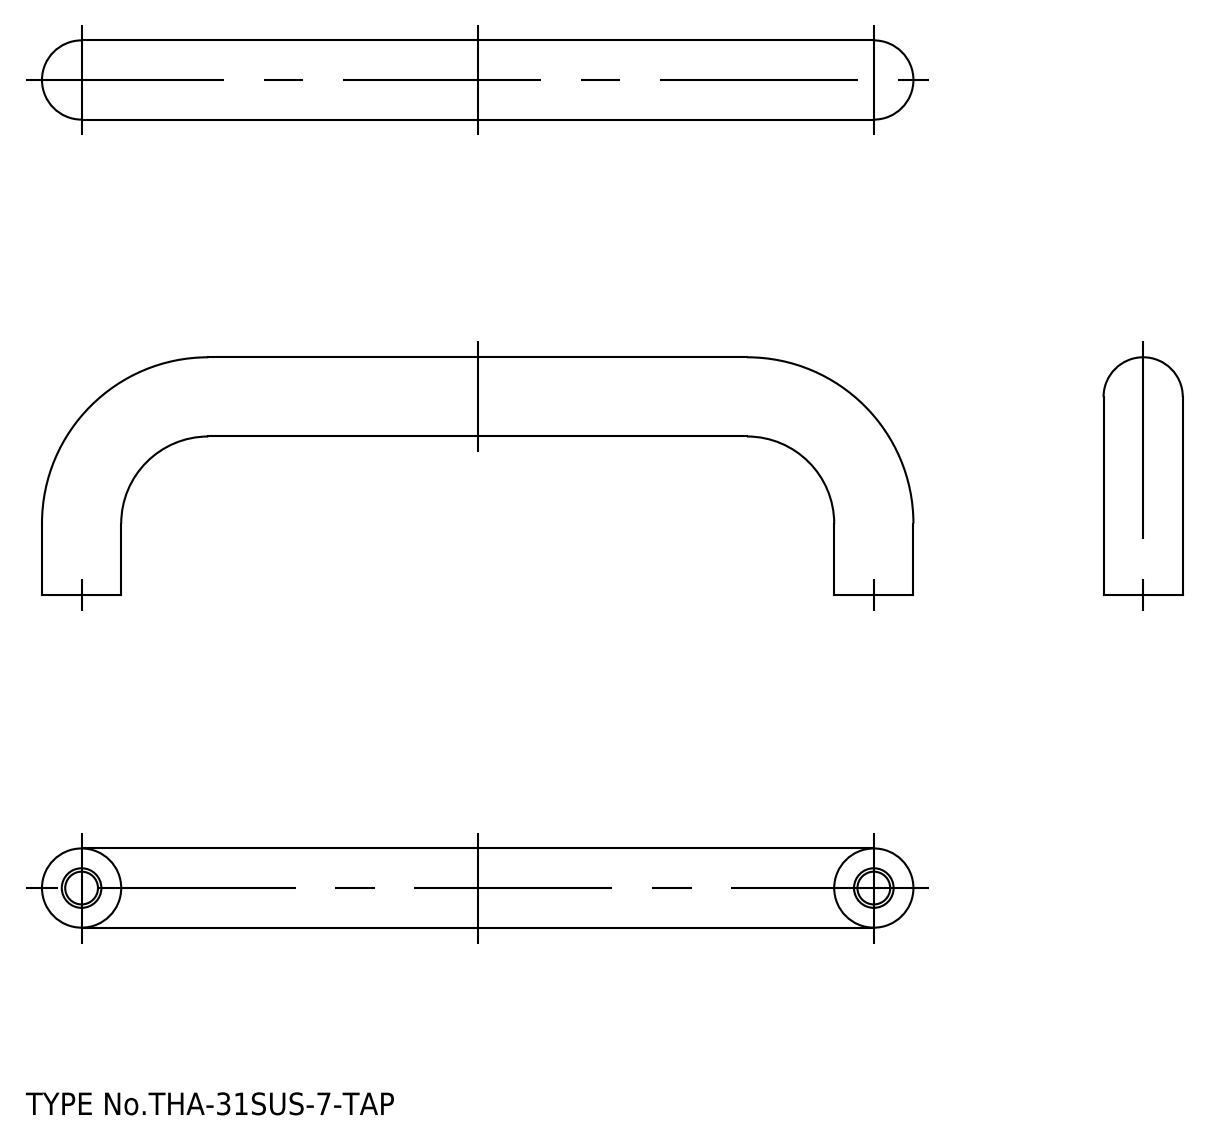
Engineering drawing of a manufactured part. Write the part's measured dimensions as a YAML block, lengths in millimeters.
step_written_by: "spGate 17.5.2 (AUTOMOTIVE_DESIGN)"
units: millimeters
bodies: {solids: 1, faces: 18, planar: 4, cylindrical: 10, other: 4}
overall_size: [110, 30, 10]
volume: 10274
surface_area: 4786
round_holes:
  - {diameter: 5, count: 2}
round_bosses_or_shafts:
  - {diameter: 10, count: 3}
face_to_face_distances: [11]
hole_center_spacings: [100]
